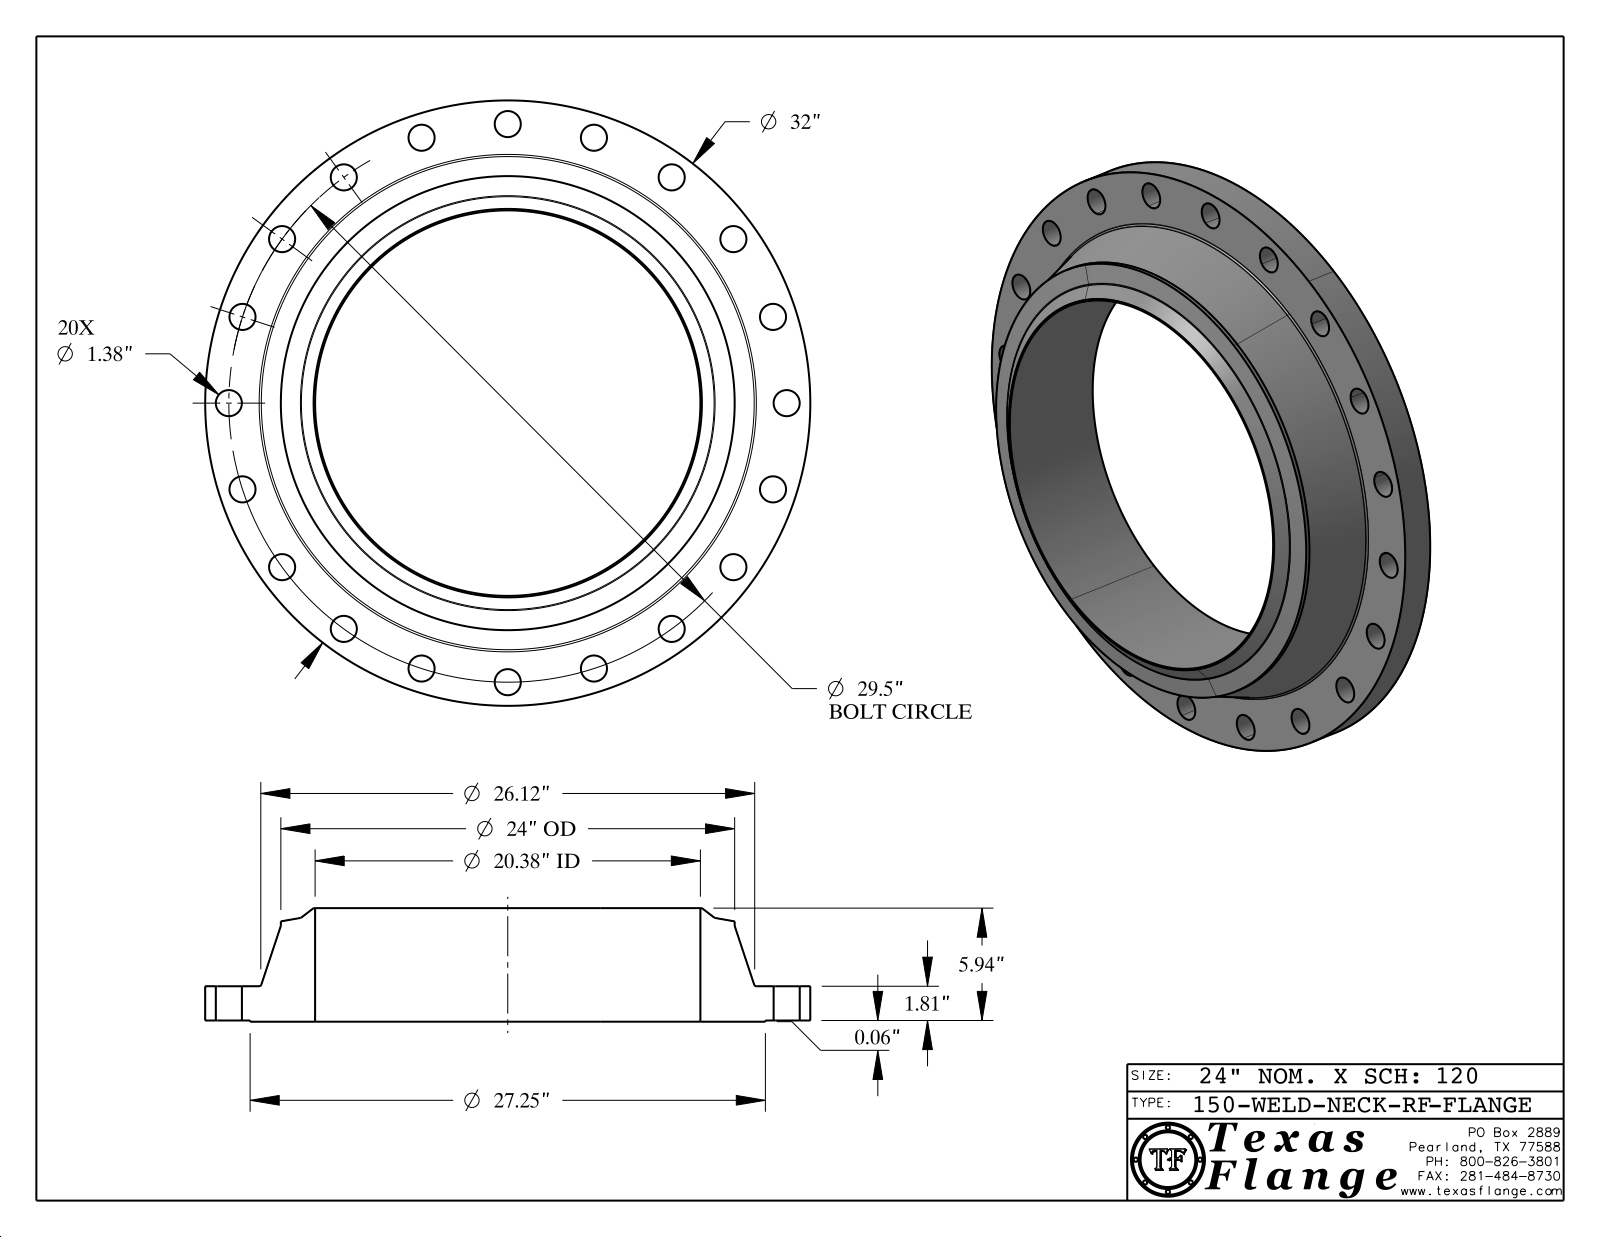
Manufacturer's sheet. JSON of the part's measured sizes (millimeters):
{"part_name": "150-WELD-NECK-RF", "step_written_by": "CATIA V5 STEP AP214 (AUTOMOTIVE_DESIGN)", "units": "millimeters", "bodies": {"solids": 1, "faces": 447, "planar": 369, "cylindrical": 68, "other": 10}, "overall_size": [812.8, 812.8, 152.5], "volume_mm3": 23300000, "surface_area_mm2": 1184000, "round_holes": [[35.1, 20], [12.6, 1], [517.6, 1]], "round_bosses_or_shafts": [[0.8, 8], [812.8, 1], [692.2, 1], [609.6, 1], [9.9, 1]], "face_to_face_distances": [47.5, 1.6, 46, 152.5, 150.9, 104.9, 47.2, 45.6, 0.4, 105.3], "hole_center_spacings": [374.7, 740.1, 117.2, 440.4, 529.8, 606.2, 667.6, 231.5]}
